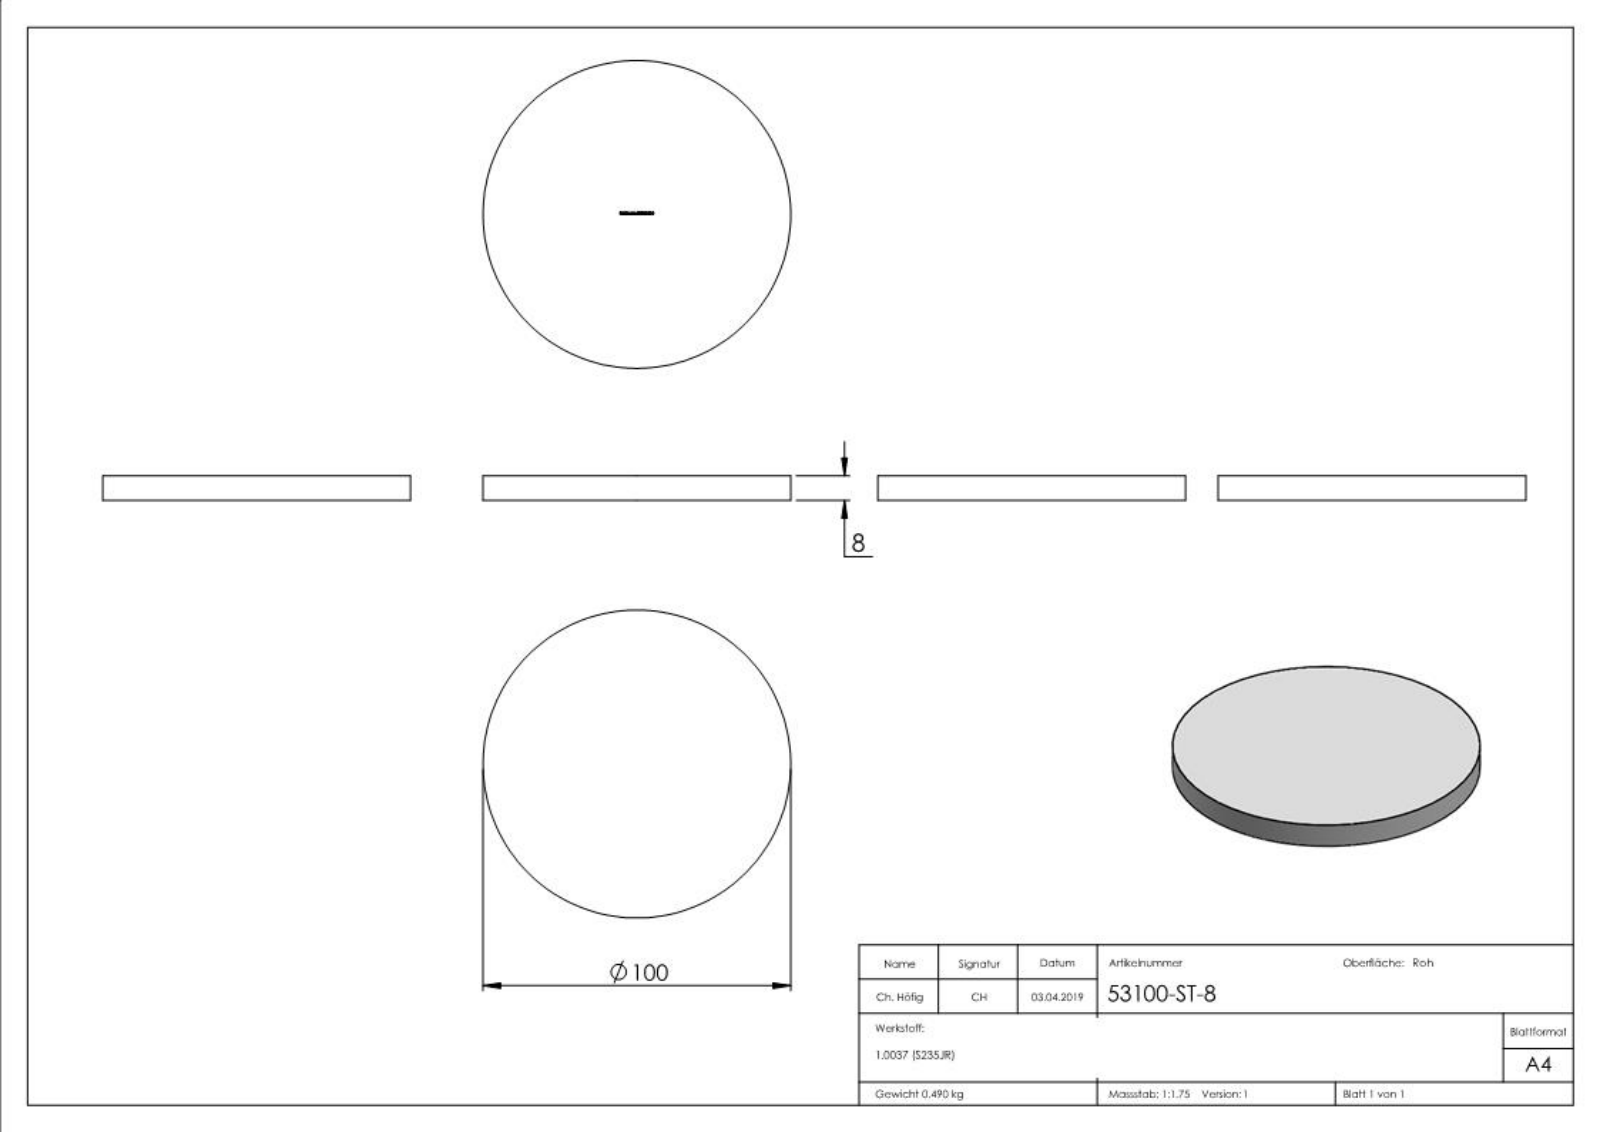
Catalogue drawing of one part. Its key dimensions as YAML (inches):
part_name: "53100-ST-8"
step_written_by: "SolidWorks 2015 (CONFIG_CONTROL_DESIGN)"
units: inches
bodies: {solids: 1, faces: 236, planar: 114, cylindrical: 2, other: 120}
overall_size: [3.937, 3.937, 0.315]
volume: 3.834
surface_area: 28.25
round_bosses_or_shafts:
  - {diameter: 3.937, count: 1}
face_to_face_distances: [0.315, 0.311, 0.07, 0.017, 0.033, 0.03, 0.031, 0.039, 0.23, 0.048]
